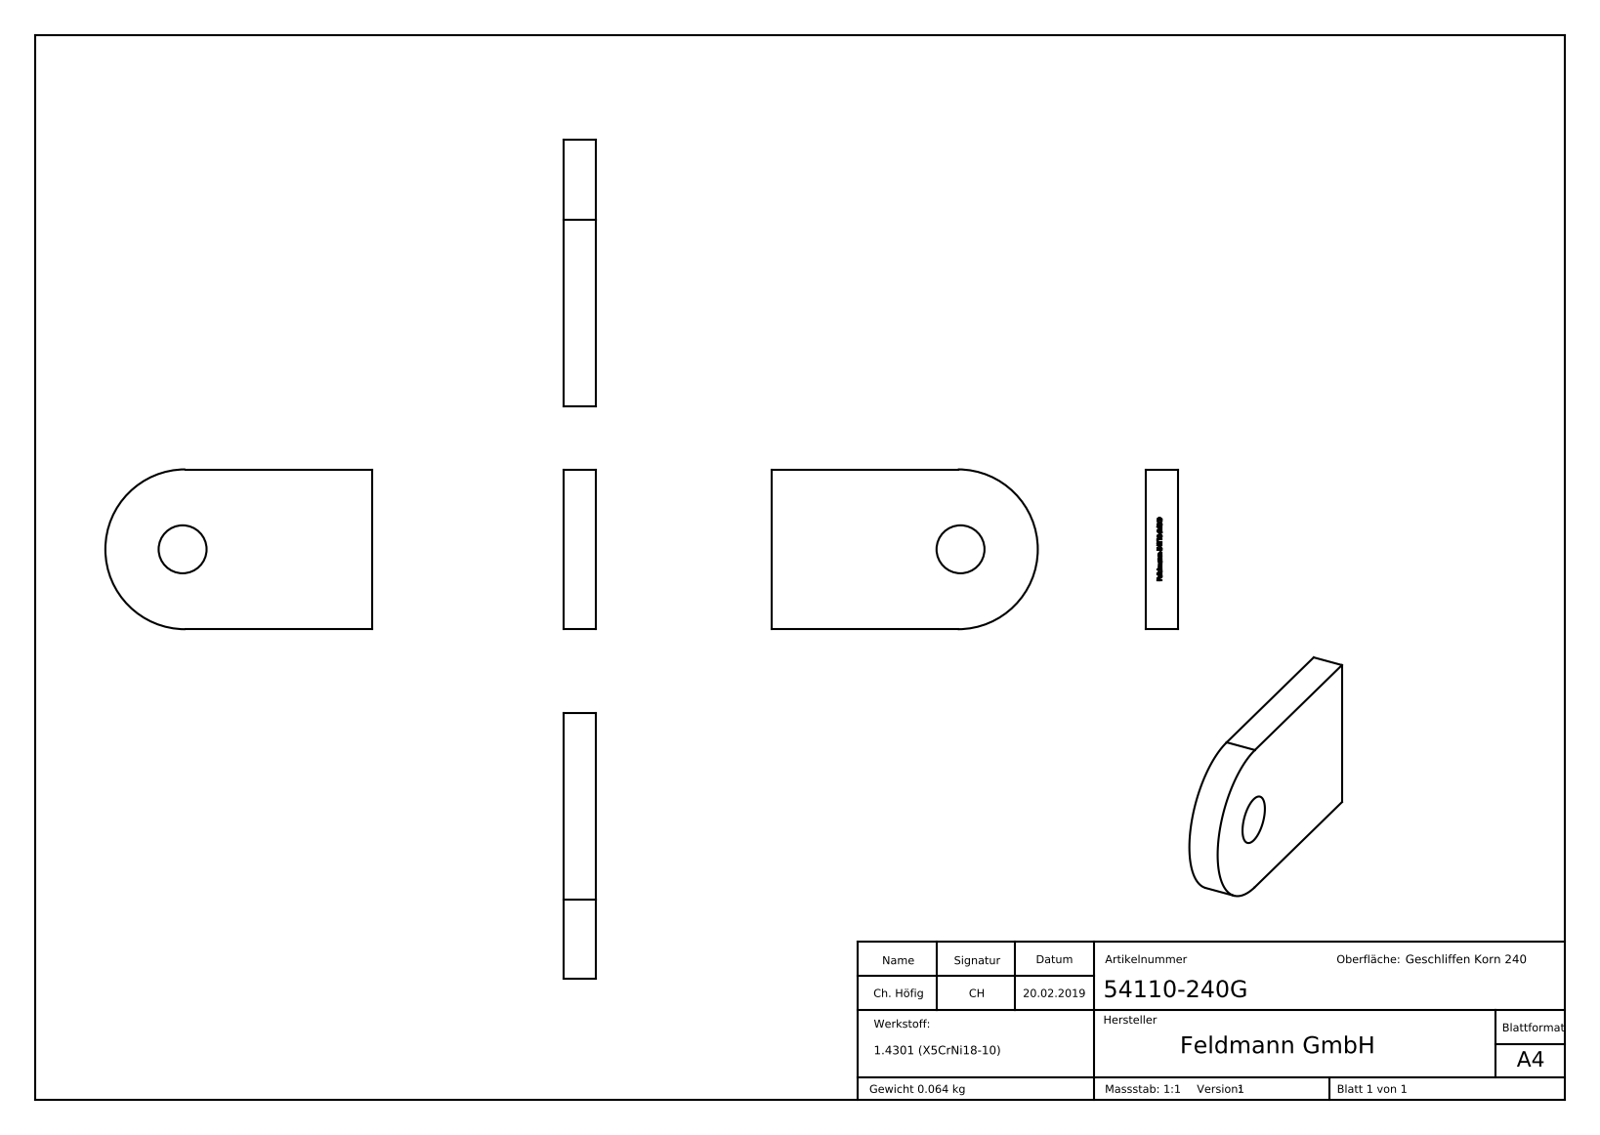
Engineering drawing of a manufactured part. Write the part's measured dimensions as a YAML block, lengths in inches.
part_name: "54110-240G"
step_written_by: "SolidWorks 2015 (CONFIG_CONTROL_DESIGN)"
units: inches
bodies: {solids: 1, faces: 235, planar: 142, cylindrical: 4, other: 89}
overall_size: [1.969, 1.181, 0.236]
volume: 0.491
surface_area: 5.794
round_holes:
  - {diameter: 0.354, count: 1}
partial_cylinders:
  - {radius: 0.591, count: 1}
face_to_face_distances: [0.236, 1.181, 0.118, 0.111, 0.024, 0.021, 0.019, 0.23, 0.254, 0.094]
